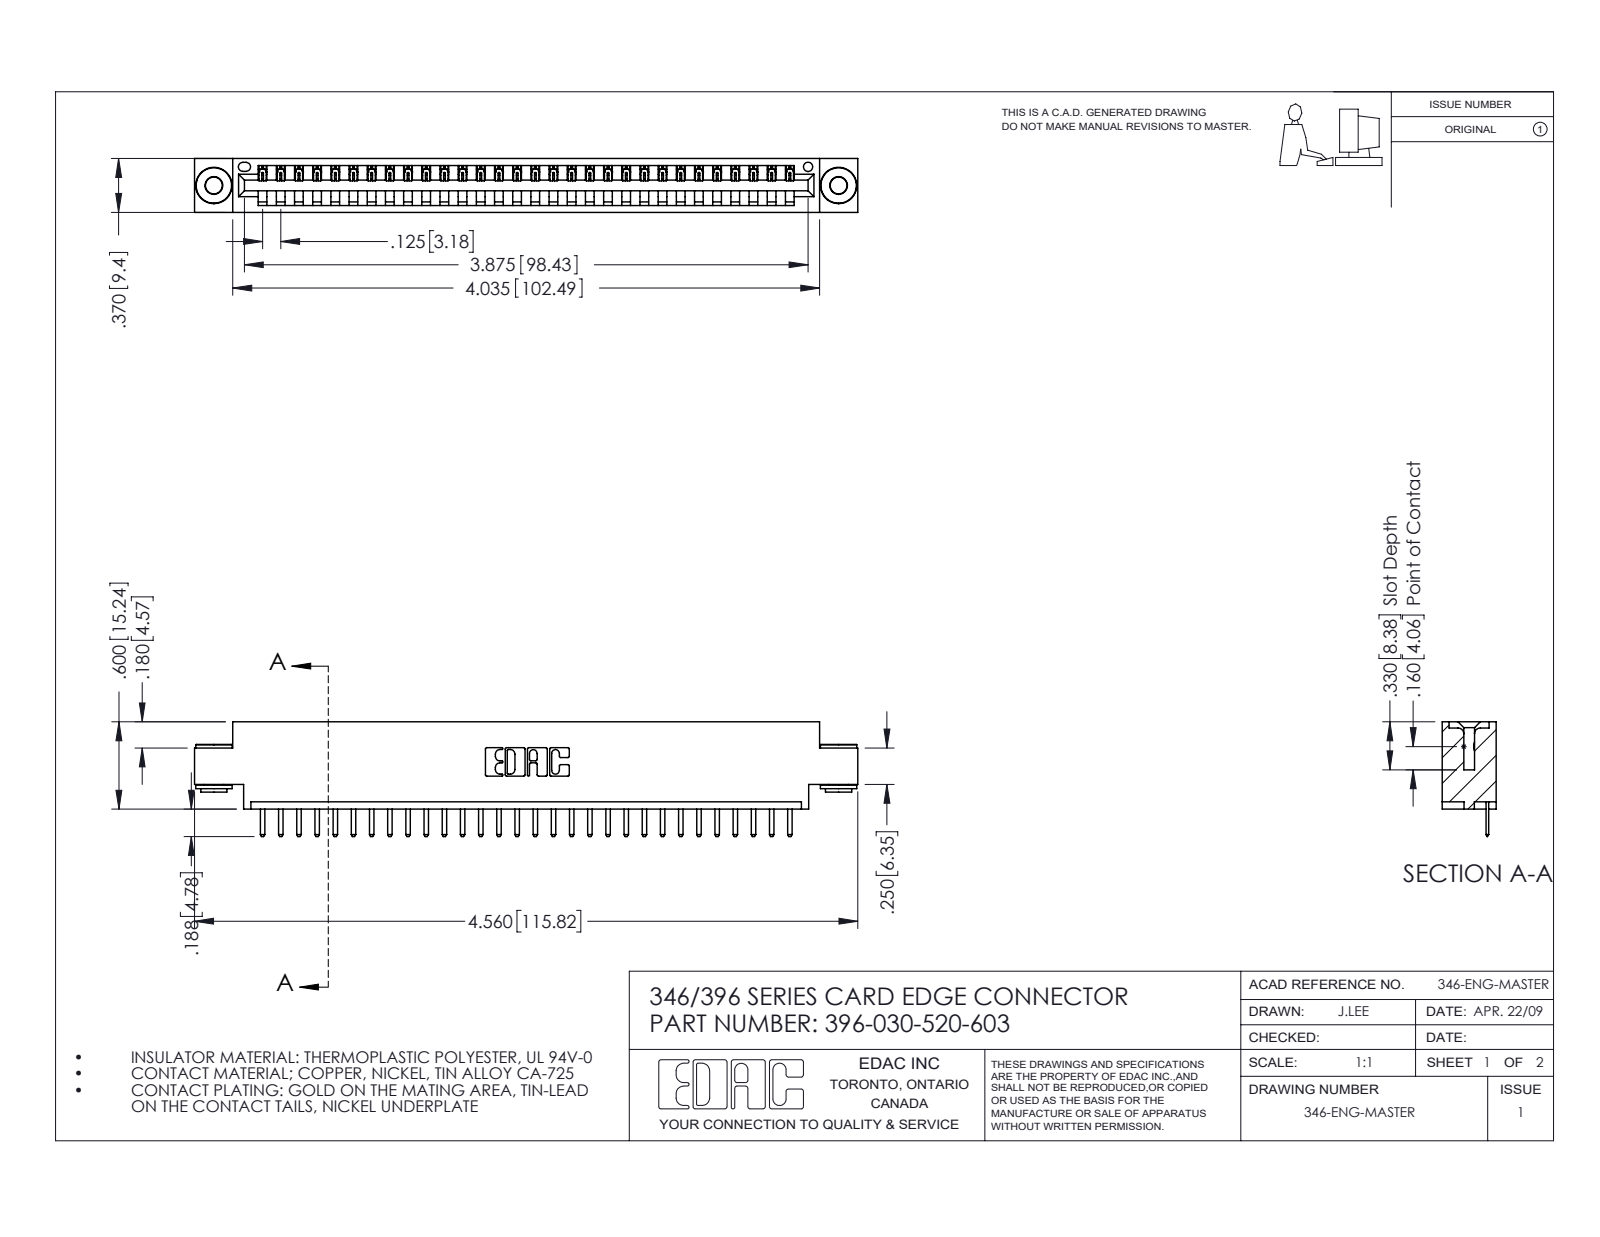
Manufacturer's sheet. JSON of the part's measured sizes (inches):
{"part_name": "345-250-002_345-250-002-102; 396-030-520-603; 345-292-001_345-293-120; 346 Part_0.170 Offset - 0.156 Dia-TH", "step_written_by": "SolidWorks 2016 (CONFIG_CONTROL_DESIGN)", "units": "inches", "bodies": {"solids": 33, "faces": 2024, "planar": 1350, "cylindrical": 666, "other": 8}, "overall_size": [4.56, 0.788, 0.37], "volume_in3": 0.658, "surface_area_in2": 20.83, "round_holes": [[0.116, 2], [0.156, 2], [0.064, 1]], "round_bosses_or_shafts": [[0.25, 2], [0.18, 2], [0.136, 2]], "partial_cylinders_radius": [[0.01, 62], [0.006, 60], [0.01, 22], [0.007, 6], [0.031, 6], [0.026, 3], [0.031, 2], [0.04, 2]], "face_to_face_distances": [0.048, 0.322, 0.37, 0.25, 0.025, 0.148, 0.222, 0.1, 0.174, 0.072], "hole_center_spacings": [0.246, 4.087, 4.295]}
